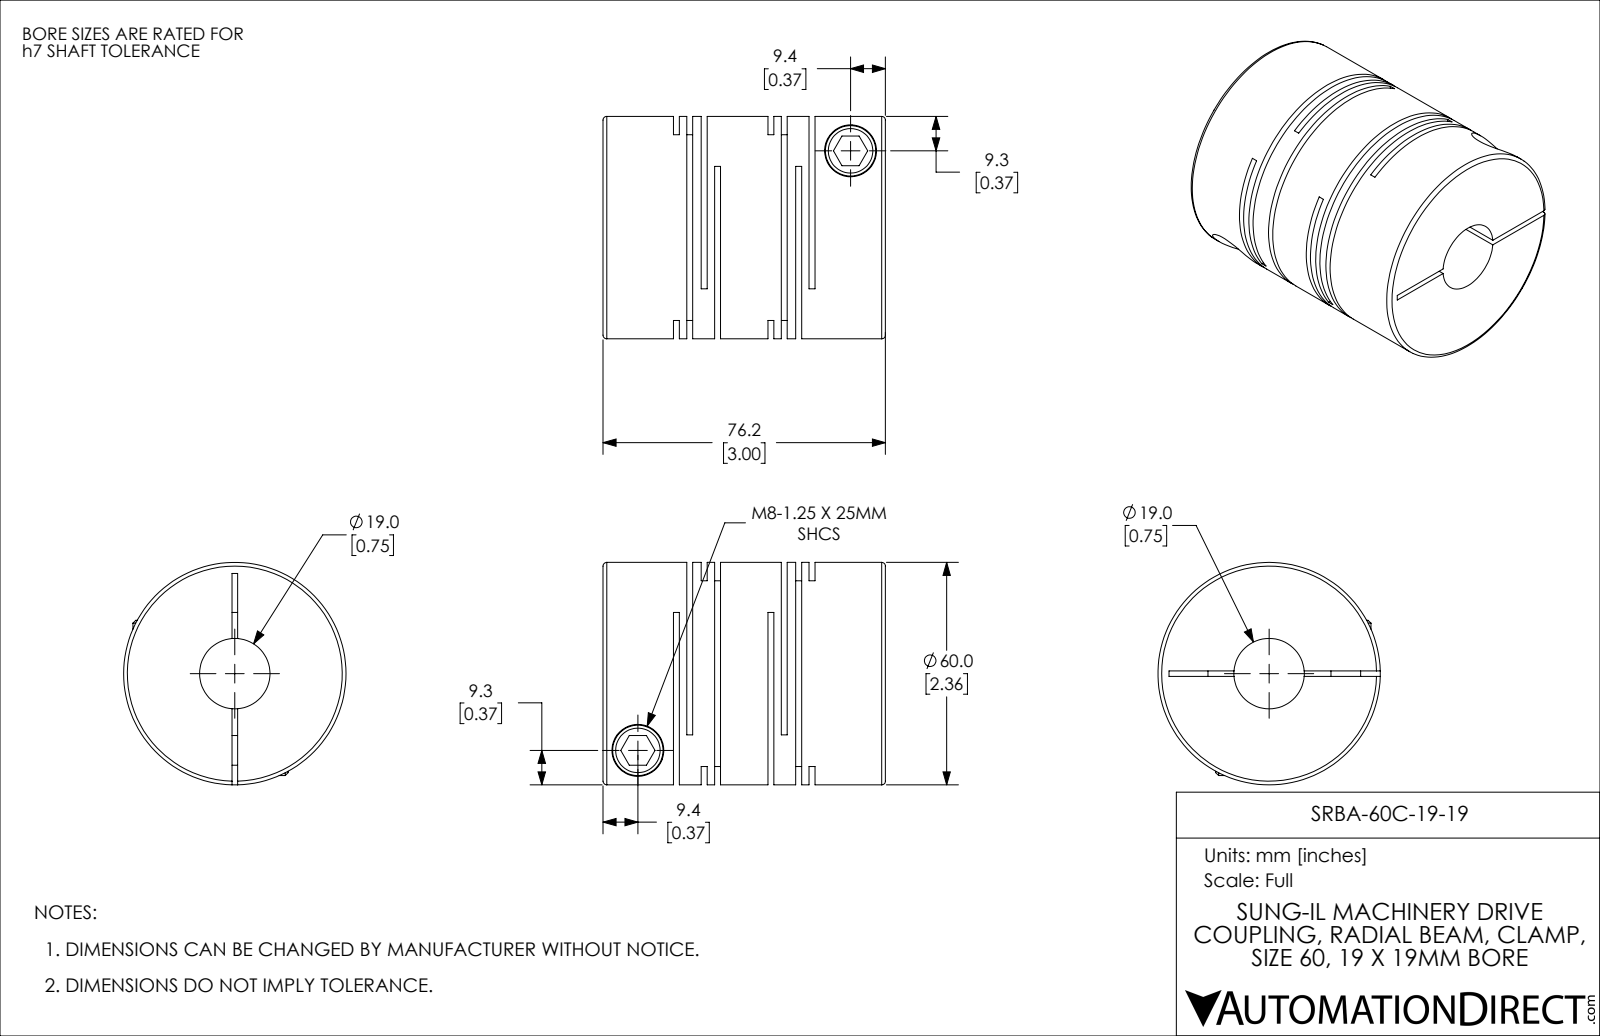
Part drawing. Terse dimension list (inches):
name: SRBA-60C-19-19
written by: SolidWorks 2021 (CONFIG_CONTROL_DESIGN)
unit: in
bodies: 1 solid, 115 faces (60 planar, 42 cylindrical, 13 other)
size: 3 × 2.362 × 2.362
volume: 9.896 in³; area: 92.29 in²
holes: 2× ⌀0.315, 2× ⌀0.551, 1× ⌀0.748
bosses: 2× ⌀0.535, 1× ⌀2.362
face distances: 0.063, 0.295, 0.142, 1.004, 1.299, 0.709, 0.079, 0.232, 0.941, 0.154
